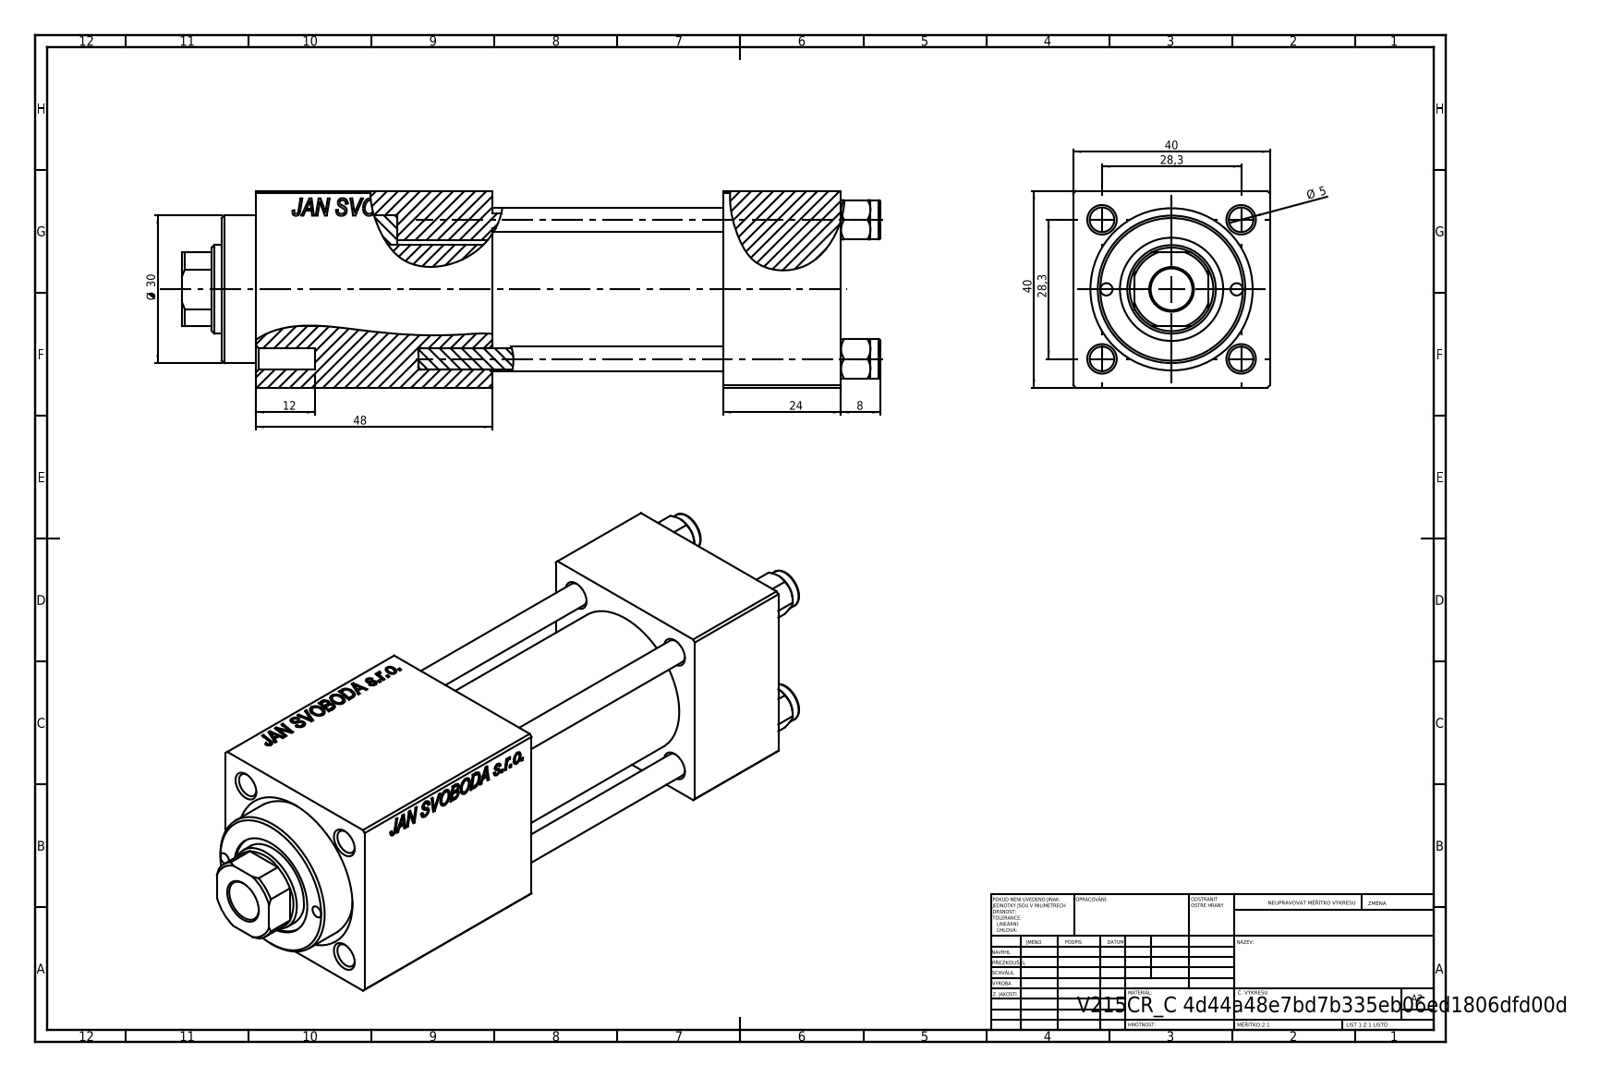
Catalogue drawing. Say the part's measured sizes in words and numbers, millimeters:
The part is named "NUT_M5_C; V215CR_C_TYCINKA; V215CR_C_Body; V215_VC_A (+1 more)". Its 3-D file was written by "SolidWorks 2019 (CONFIG_CONTROL_DESIGN)". It is 11 solids with 1150 faces: 526 planar, 88 cylindrical and 536 other. Overall it measures 142 by 40 by 40 millimeters. Its volume is 149 878 cubic millimeters and its surface area 56 906 square millimeters. Round holes: 4 of diameter 5, 3 of diameter 20, 2 of diameter 2.5, 2 of diameter 7, 2 of diameter 13.16, 1 of diameter 8.5, 1 of diameter 18, 1 of diameter 21, 1 of diameter 25, 1 of diameter 30. Round bosses or shafts: 4 of diameter 8, 1 of diameter 31. Partial cylindrical surfaces (rounded edges, fillets, slot ends): 1 of radius 8.5. The main face-to-face distances are 40, 24, 71, 47, 90.3, 66.3, 19.3, 48, 119, 95. The hole center spacings are 14.18, 20.01, 28.3, 30.84, 13.25, 40.02, 26.5, 72.
